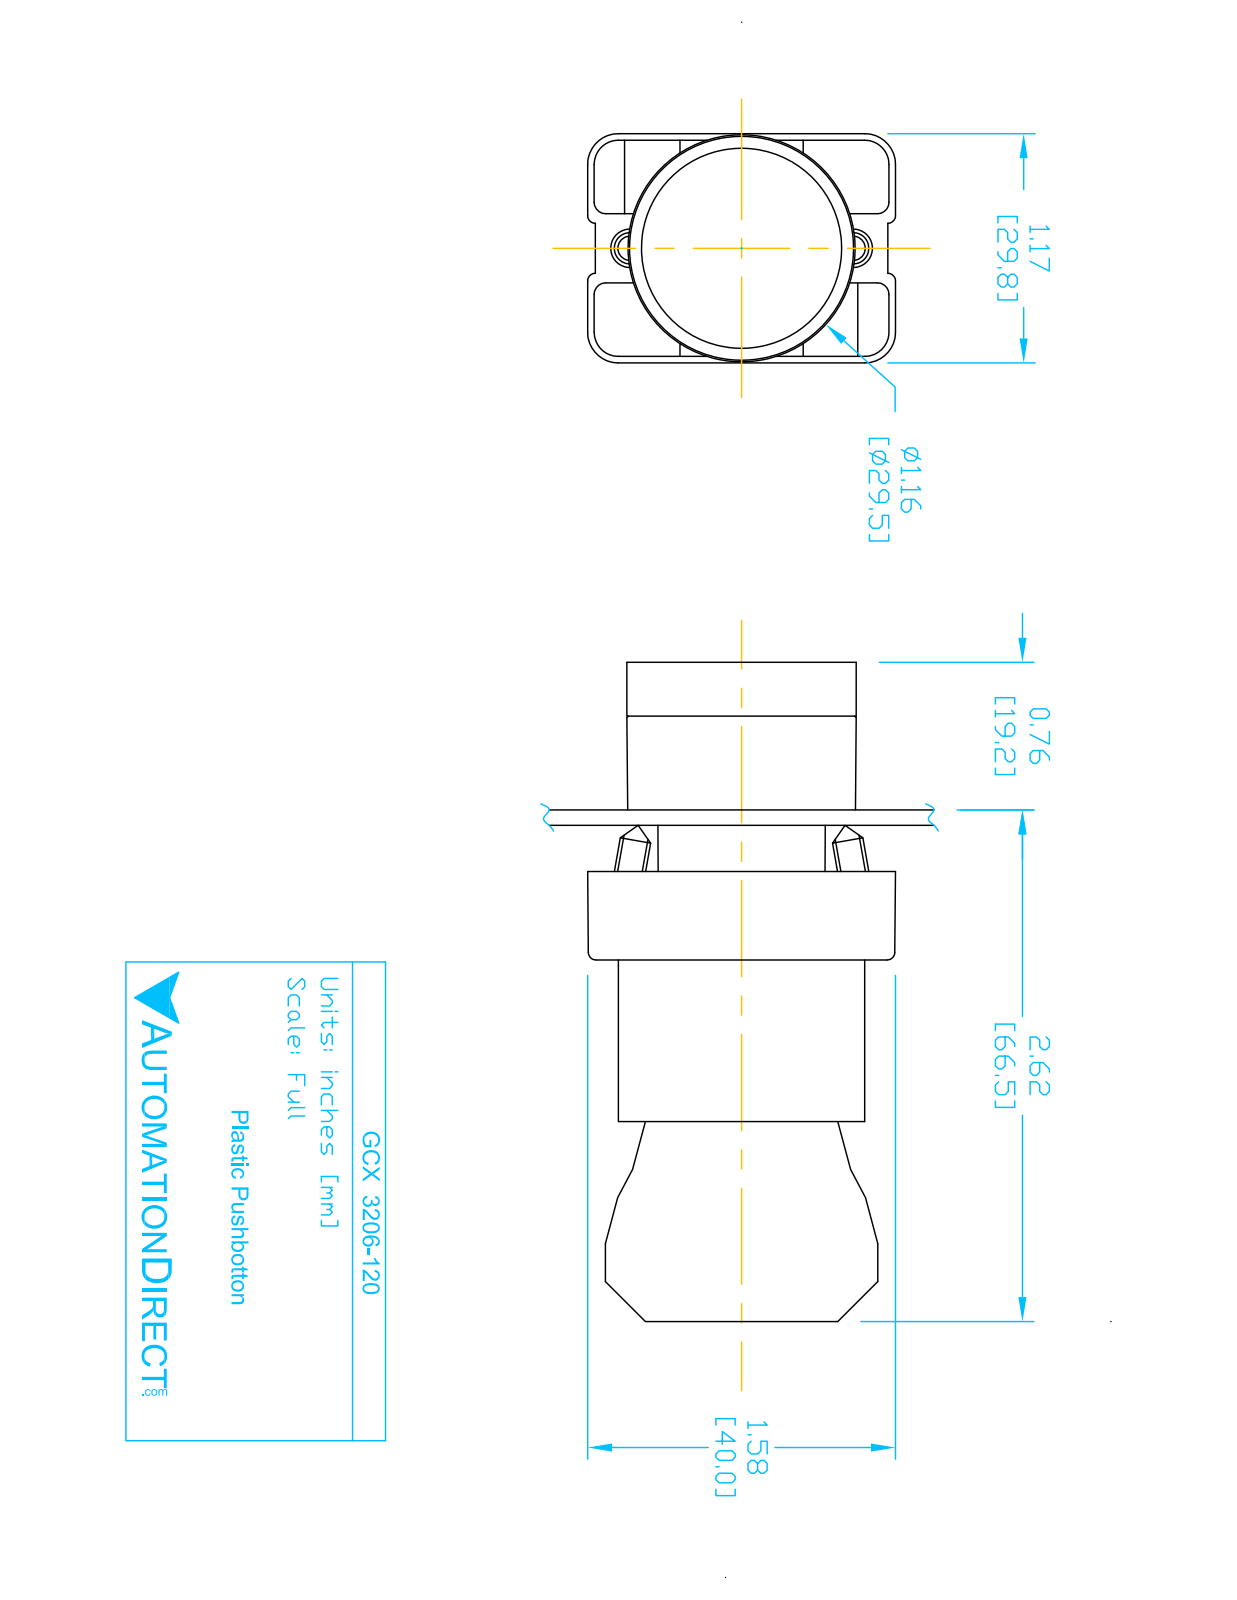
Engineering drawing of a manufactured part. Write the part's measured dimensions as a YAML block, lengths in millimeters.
part_name: "GCX3206 OPERATOR; ecx1040; ECX3029-2; GCX3206-120 (+1 more)"
step_written_by: "SolidWorks 2016 (AUTOMOTIVE_DESIGN)"
units: millimeters
bodies: {solids: 8, faces: 431, planar: 252, cylindrical: 148, other: 31}
overall_size: [84.3, 40.2, 29.9]
volume: 45790
surface_area: 25010
round_holes:
  - {diameter: 2, count: 2}
  - {diameter: 3.1, count: 2}
  - {diameter: 3.3, count: 2}
  - {diameter: 2.2, count: 1}
  - {diameter: 5, count: 1}
  - {diameter: 11.9, count: 1}
  - {diameter: 22.3, count: 1}
  - {diameter: 22.6, count: 1}
  - {diameter: 26, count: 1}
round_bosses_or_shafts:
  - {diameter: 4, count: 4}
  - {diameter: 29.8, count: 1}
  - {diameter: 25.5, count: 1}
  - {diameter: 24, count: 1}
  - {diameter: 21.7, count: 1}
  - {diameter: 19.8, count: 1}
  - {diameter: 12.8, count: 1}
partial_cylinders:
  - {radius: 1.5, count: 24}
  - {radius: 1, count: 12}
  - {radius: 3.1, count: 12}
  - {radius: 4, count: 12}
  - {radius: 1, count: 8}
  - {radius: 3.3, count: 2}
  - {radius: 0.5, count: 1}
  - {radius: 1.6, count: 1}
face_to_face_distances: [21, 14.7, 51.3, 30.3, 29.7, 7, 58.3, 37.3, 0.8, 0.8]
hole_center_spacings: [6, 13.8, 12, 12.4]
